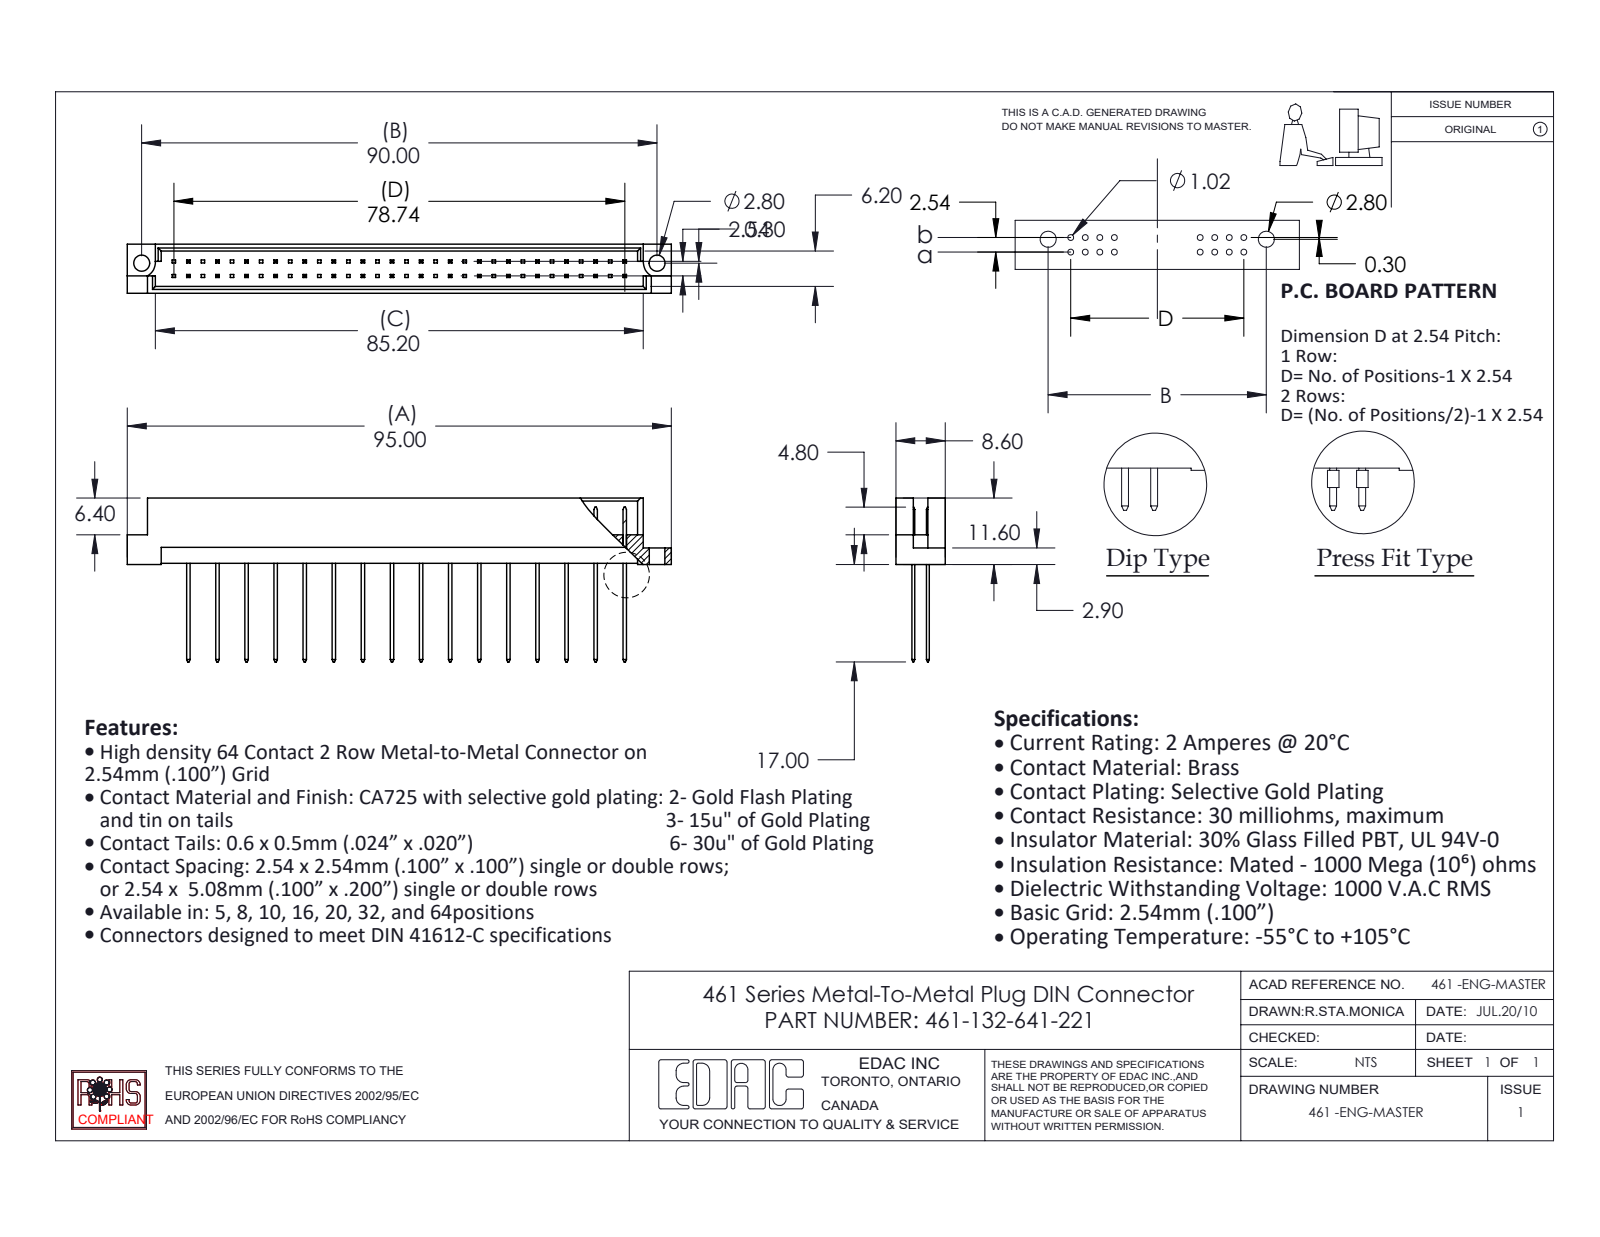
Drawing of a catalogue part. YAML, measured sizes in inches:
part_name: "461 Part_64; 461-290_41; 461-132-641-221"
step_written_by: "SolidWorks 2020 (CONFIG_CONTROL_DESIGN)"
units: inches
bodies: {solids: 33, faces: 753, planar: 746, cylindrical: 7, other: 0}
overall_size: [3.74, 1.126, 0.339]
volume: 0.3
surface_area: 11.72
round_holes:
  - {diameter: 0.11, count: 2}
partial_cylinders:
  - {radius: 0.11, count: 2}
face_to_face_distances: [0.047, 0.291, 0.339, 0.244, 0.1, 0.129, 0.209, 0.082, 0.162, 0.109]
hole_center_spacings: [3.543]
